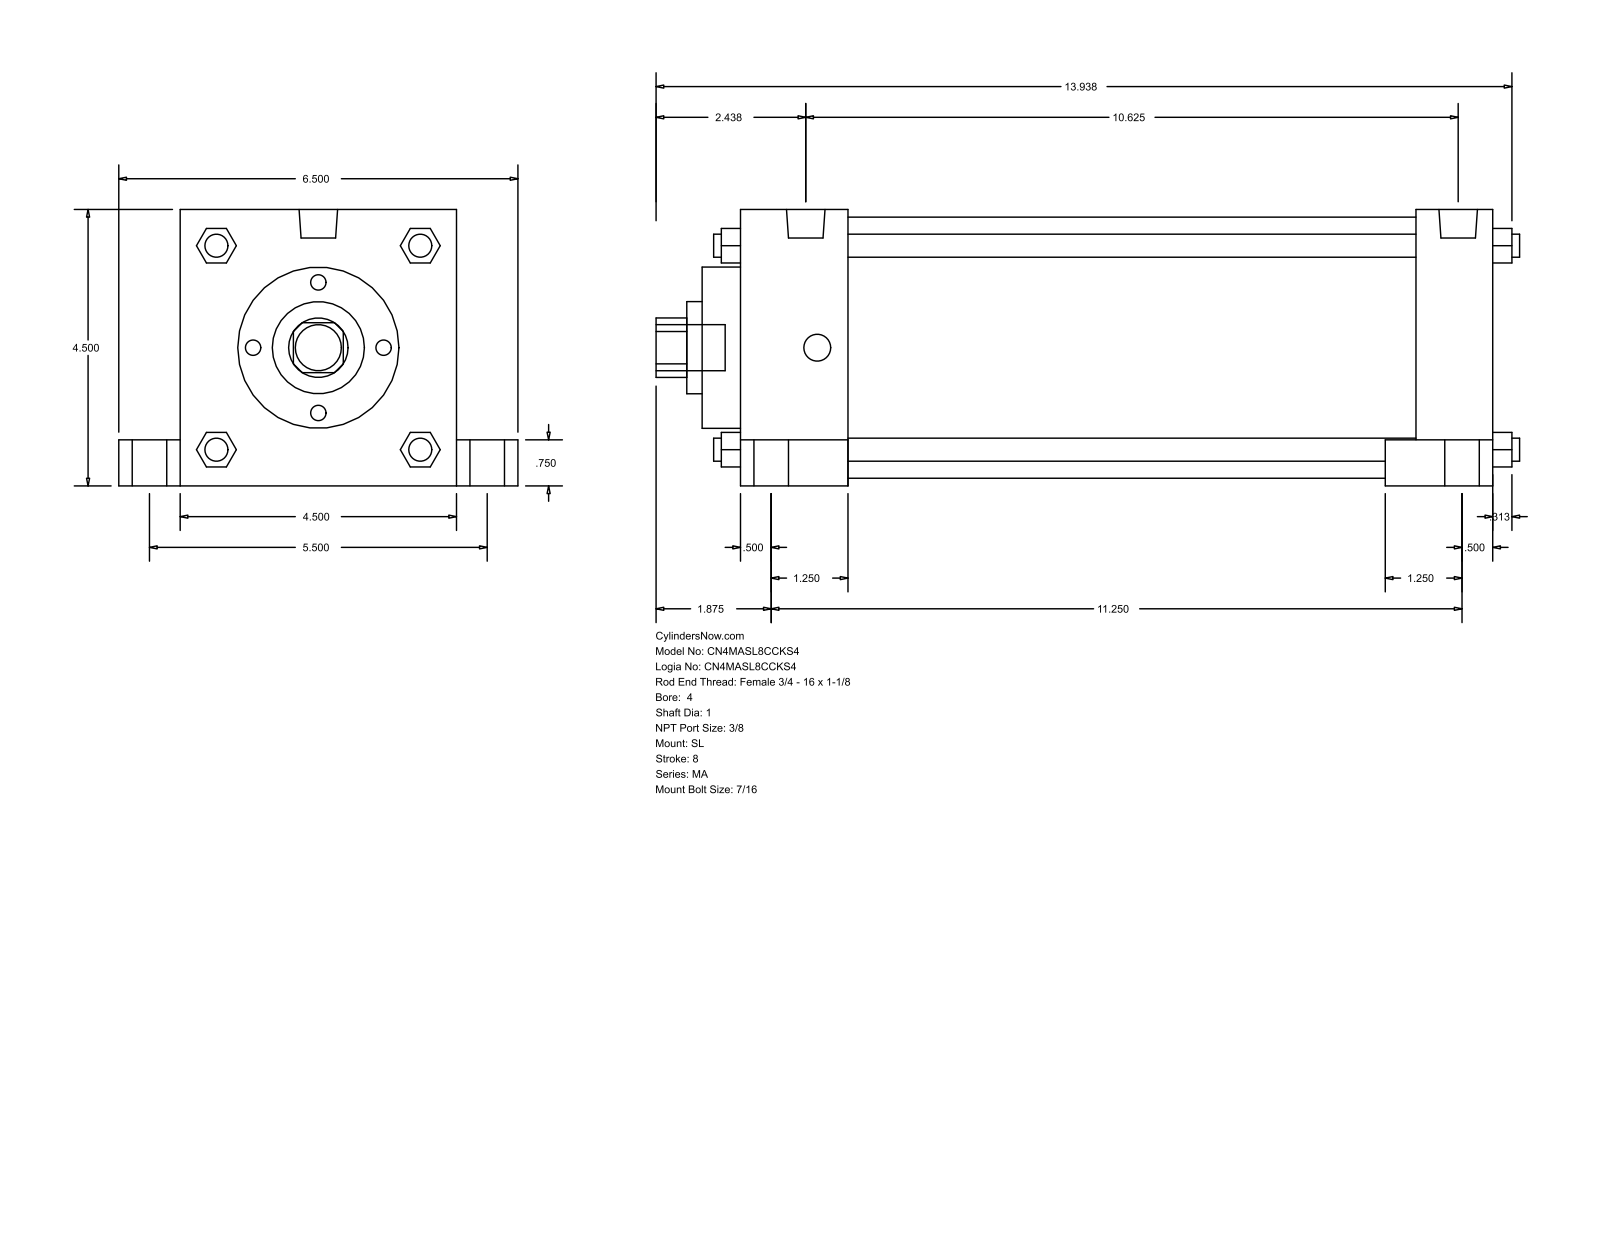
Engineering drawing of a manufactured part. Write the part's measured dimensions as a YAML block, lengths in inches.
part_name: "MA_SL__0400_1"
step_written_by: "GSSL Pune (CONFIG_CONTROL_DESIGN)"
units: inches
bodies: {solids: 0, faces: 150, planar: 113, cylindrical: 37, other: 0}
overall_size: [14.063, 6.5, 4.5]
round_holes:
  - {diameter: 1, count: 1}
  - {diameter: 1.5, count: 1}
  - {diameter: 2.625, count: 1}
  - {diameter: 4.25, count: 1}
round_bosses_or_shafts:
  - {diameter: 0.813, count: 4}
  - {diameter: 0.563, count: 4}
  - {diameter: 0.437, count: 4}
  - {diameter: 0.375, count: 4}
  - {diameter: 0.627, count: 2}
  - {diameter: 0.75, count: 1}
partial_cylinders:
  - {radius: 0.484, count: 1}
face_to_face_distances: [4.5, 12.25, 1.75, 10.5, 11, 9.25, 1.25, 1, 5.5, 12.875]
